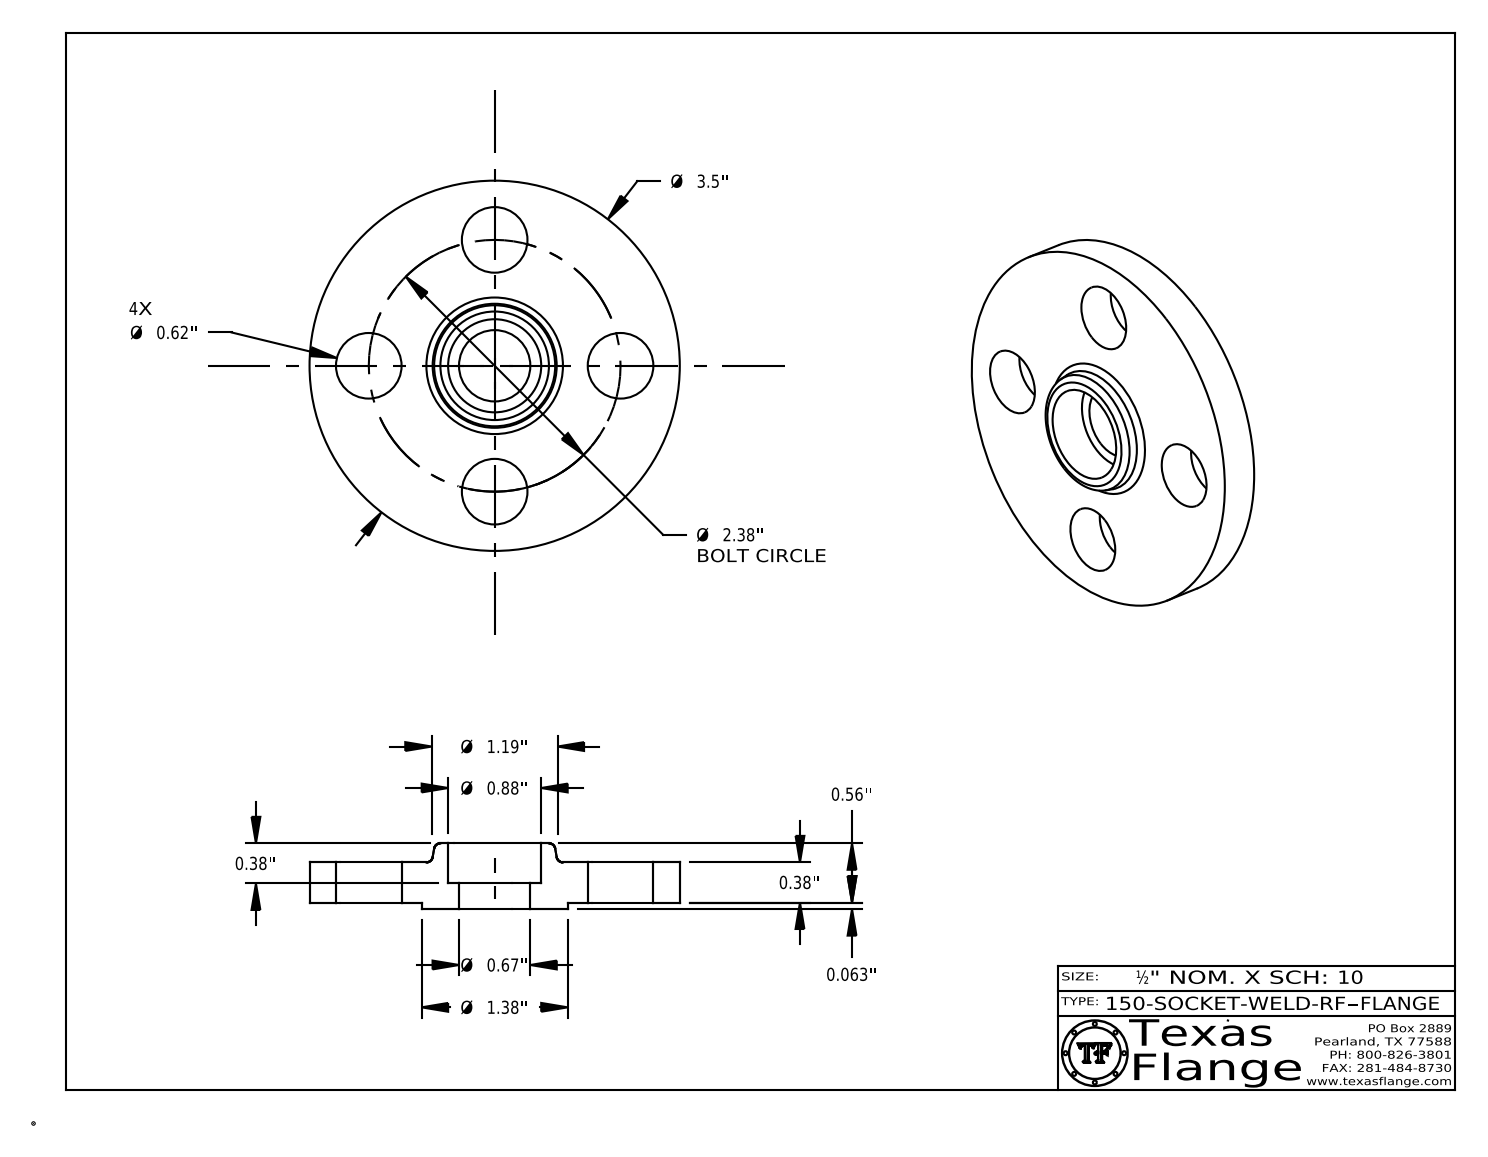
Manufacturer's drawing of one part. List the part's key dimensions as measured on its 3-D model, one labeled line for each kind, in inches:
Part name (STEP PRODUCT): 150-SOCKET-WELD-RF
STEP written by: CATIA V5 STEP AP214 (AUTOMOTIVE_DESIGN)
Units: inches
Bodies: 1 solid, 412 faces (370 planar, 36 cylindrical, 6 other)
Overall size (bounding box): 3.5 × 3.5 × 0.623
Volume: 3.162 in³ · Surface area: 25.61 in²
Round holes (diameter × count): ⌀0.62 ×4, ⌀0.495 ×1, ⌀0.674 ×1, ⌀0.88 ×1
Round bosses / shafts (diameter × count): ⌀0.03 ×8, ⌀3.5 ×1, ⌀1.38 ×1, ⌀0.39 ×1
Main face-to-face distances: 0.38, 0.063, 0.443, 0.18, 0.243, 0.2, 0.622, 0.56, 0.428, 0.365
Hole centre spacings: 1.19, 1.683, 0.911, 2.199, 2.38, 1.19
